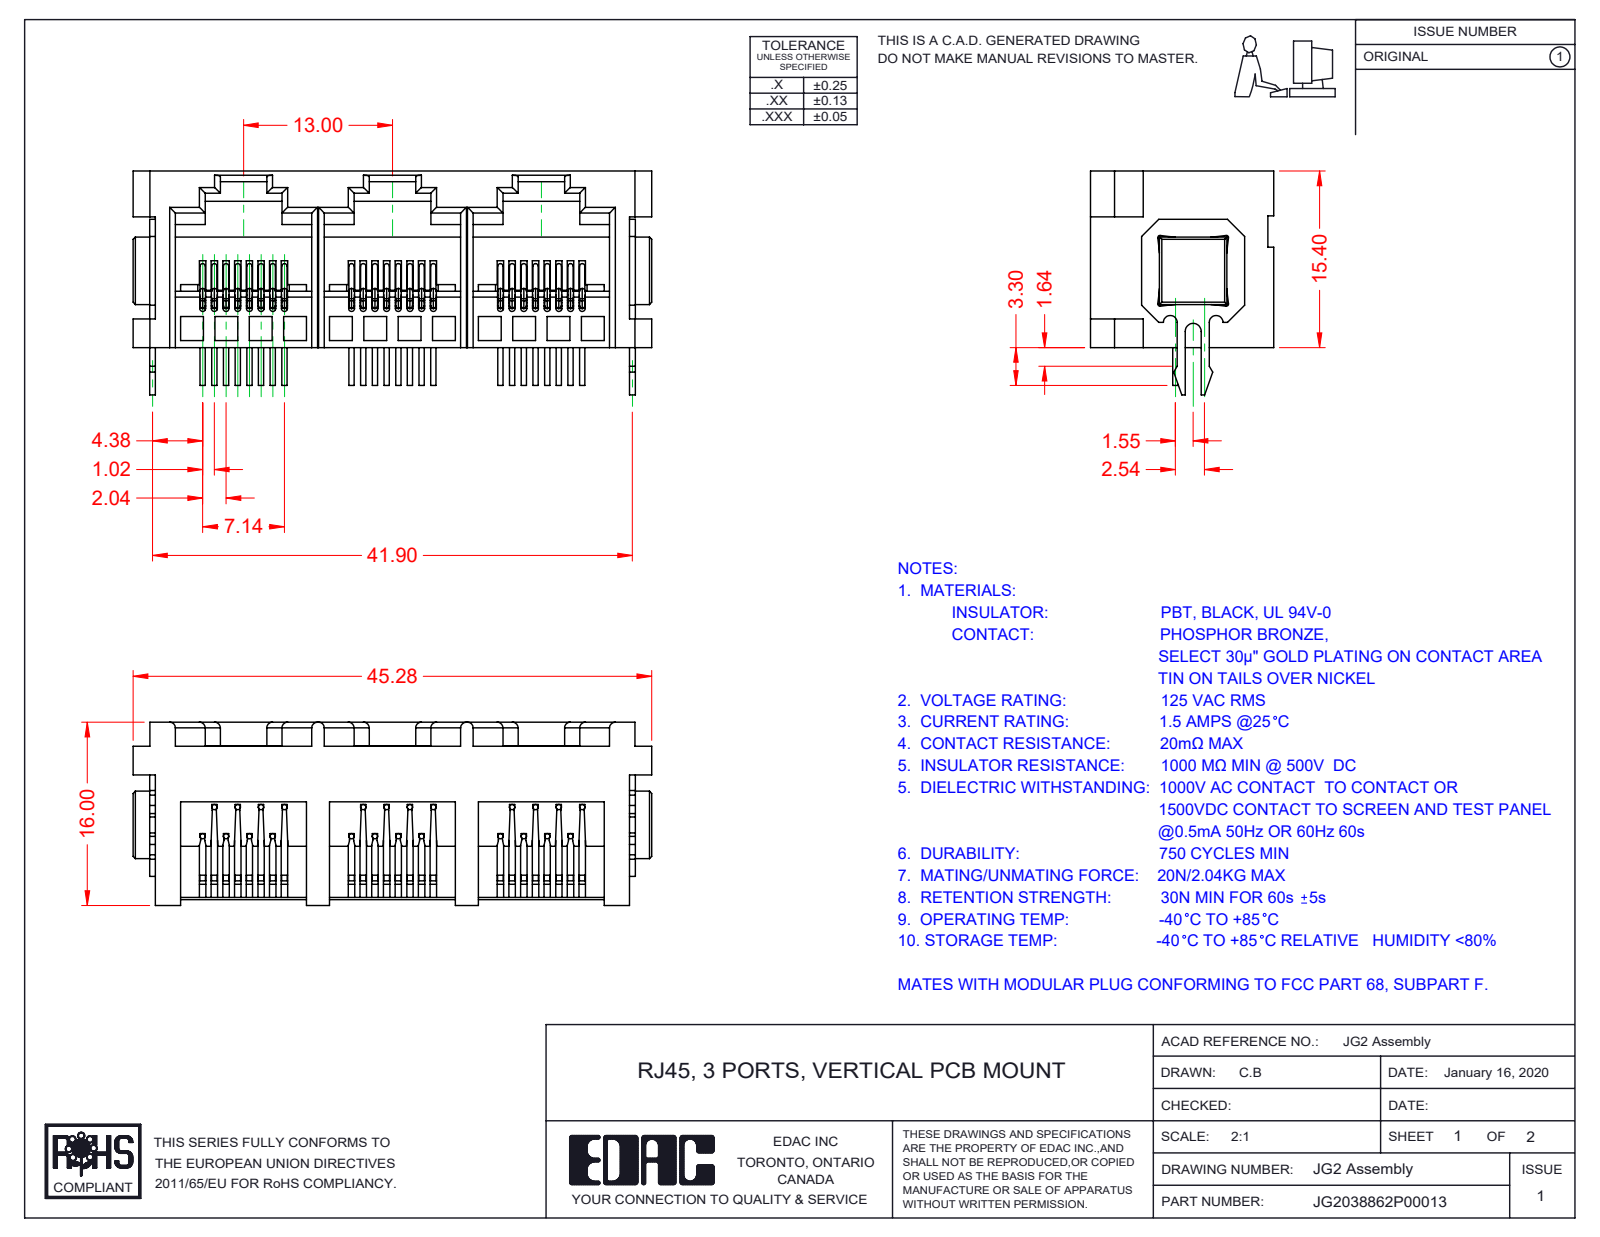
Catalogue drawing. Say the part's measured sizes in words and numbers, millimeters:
The part is named "G2 Insulator; G2 Boardlock1; G2 Boardlock2; G2 Contact Lock (+2 more)". Its 3-D file was written by "SolidWorks 2016 (CONFIG_CONTROL_DESIGN)". It is 30 solids with 1835 faces: 1210 planar, 457 cylindrical and 168 other. Overall it measures 45.28 by 19.54 by 16 millimeters. Its volume is 4 876 cubic millimeters and its surface area 9 571 square millimeters. Round bosses or shafts: 96 of diameter 0.46. Partial cylindrical surfaces (rounded edges, fillets, slot ends): 69 of radius 0.5, 4 of radius 0.2, 4 of radius 20.35, 3 of radius 0.3, 2 of radius 0.6, 1 of radius 0.21, 1 of radius 0.45, 1 of radius 0.7. The main face-to-face distances are 13, 12, 0.5, 3.4, 2.2, 11.08, 0.92, 26, 11, 2.
